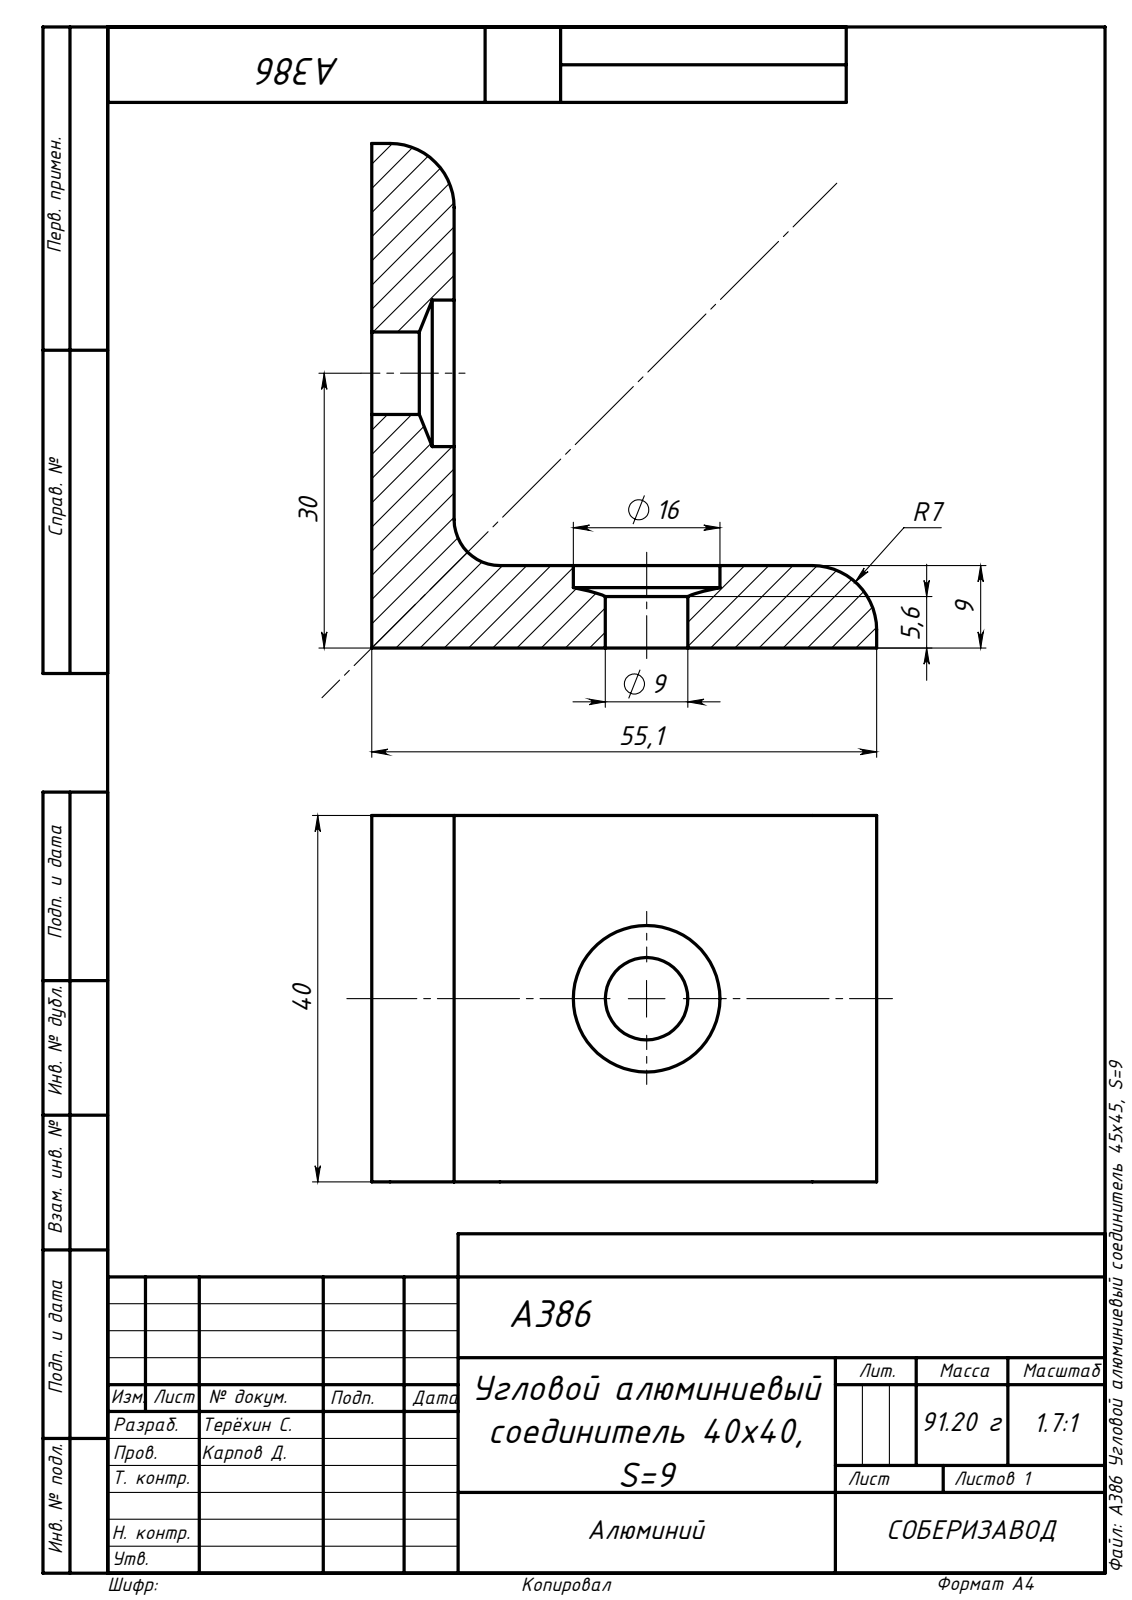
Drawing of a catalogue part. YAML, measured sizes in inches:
part_name: "A386 Угловой алюминиевый соединитель 45х45, S=9"
step_written_by: "SolidWorks 2020 (AUTOMOTIVE_DESIGN)"
units: inches
bodies: {solids: 1, faces: 23, planar: 8, cylindrical: 11, other: 4}
overall_size: [2.169, 2.169, 1.575]
volume: 2.066
surface_area: 16.41
round_holes:
  - {diameter: 0.354, count: 2}
  - {diameter: 0.63, count: 2}
partial_cylinders:
  - {radius: 0.276, count: 2}
  - {radius: 0.197, count: 1}
face_to_face_distances: [0.354, 1.575, 2.169, 1.815]
